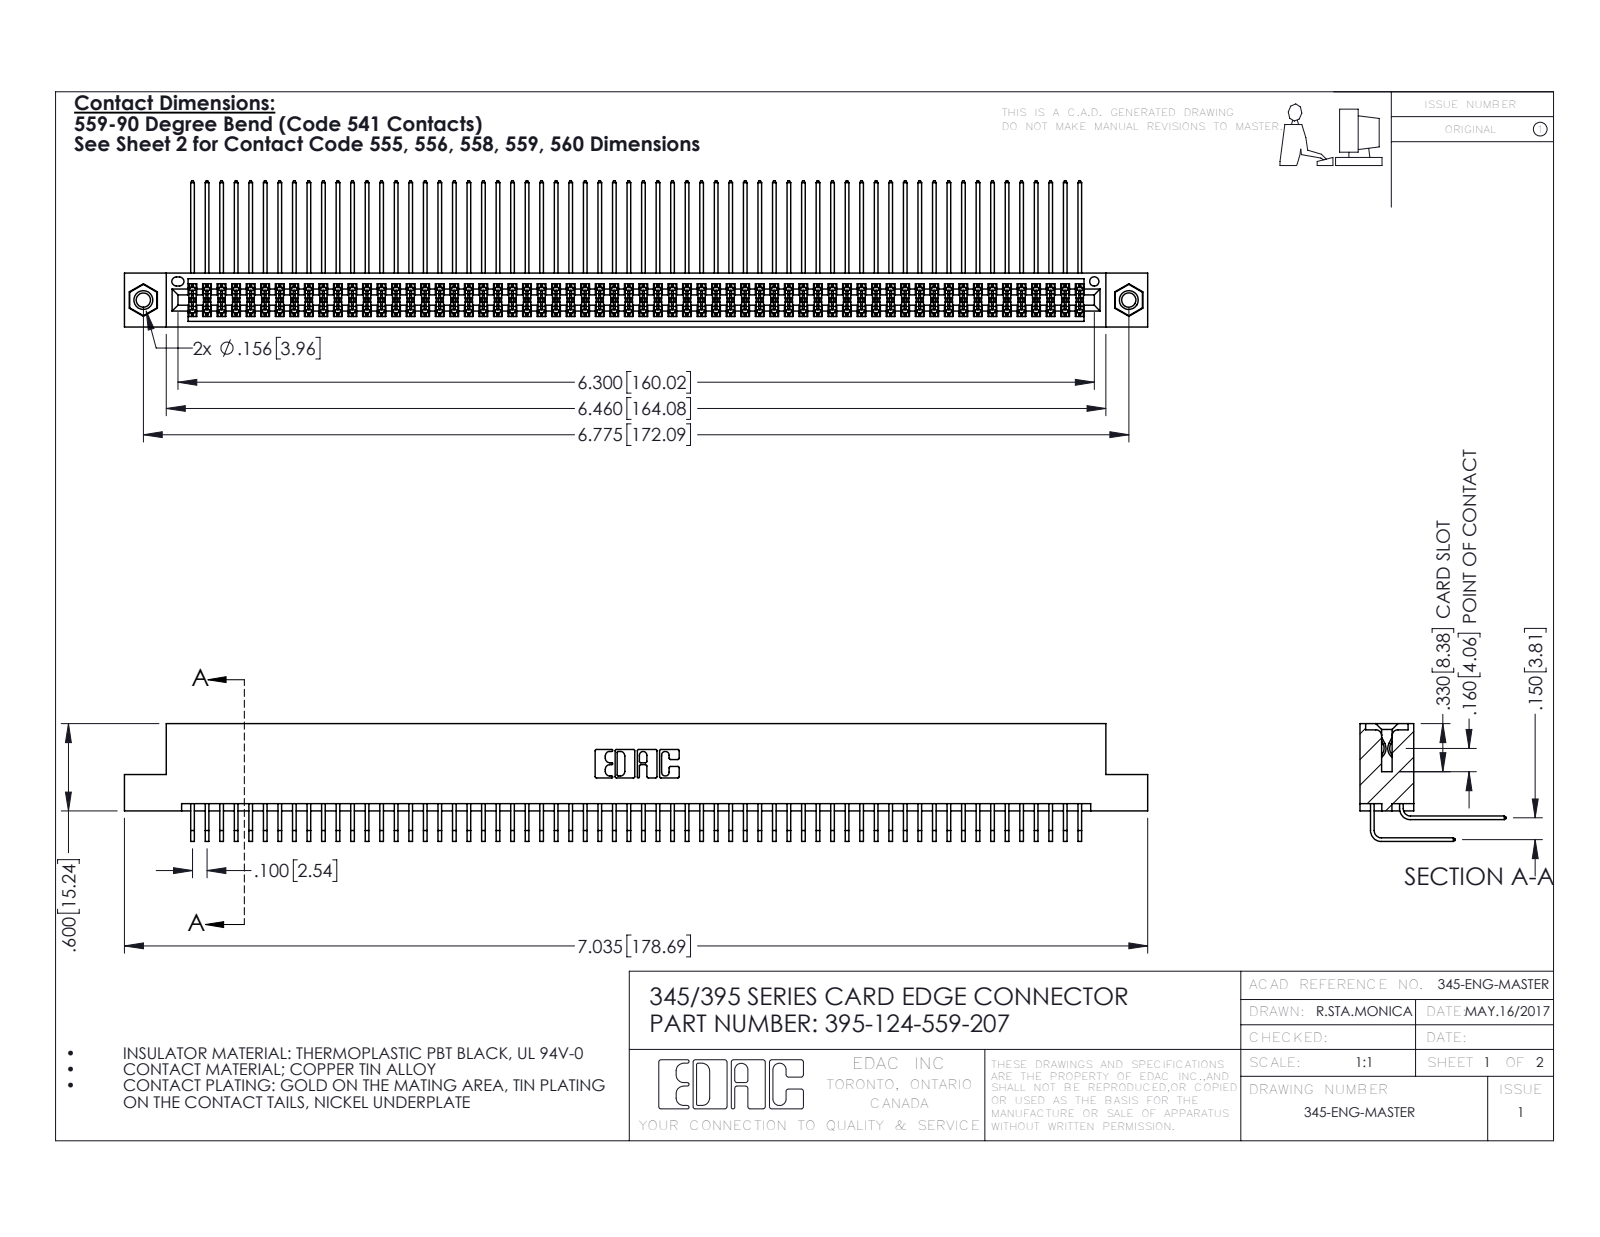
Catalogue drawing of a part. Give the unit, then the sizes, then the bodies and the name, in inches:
Units: inches
Overall size (bounding box): 7.035 × 1.005 × 0.809
Round holes (diameter × count): ⌀0.098 ×2, ⌀0.125 ×2, ⌀0.156 ×2, ⌀0.064 ×1
Round bosses / shafts (diameter × count): ⌀0.155 ×2
Partial cylindrical surfaces — rounded edges, fillets, slot ends (radius × count): R0.006 ×186, R0.01 ×22, R0.007 ×6, R0.031 ×6, R0.026 ×3, R0.014 ×2, R0.019 ×2, R0.022 ×2
Main face-to-face distances: 0.072, 0.298, 0.2, 0.37, 0.098, 0.272, 0.025, 0.225, 0.175, 0.15
Hole centre spacings: 0.27, 6.539, 6.775
Volume: 1.113 in³ · Surface area: 47.66 in²
Bodies: 127 solids, 6634 faces (4452 planar, 2166 cylindrical, 16 other)
Part name (STEP PRODUCT): 345-292-001_559 Tail - 2; 395-124-559-207; 345-250-001_345-250-005-103; 345-292-001_558 559 Tail - 1 (+1 more)
STEP written by: SolidWorks 2016 (CONFIG_CONTROL_DESIGN)
